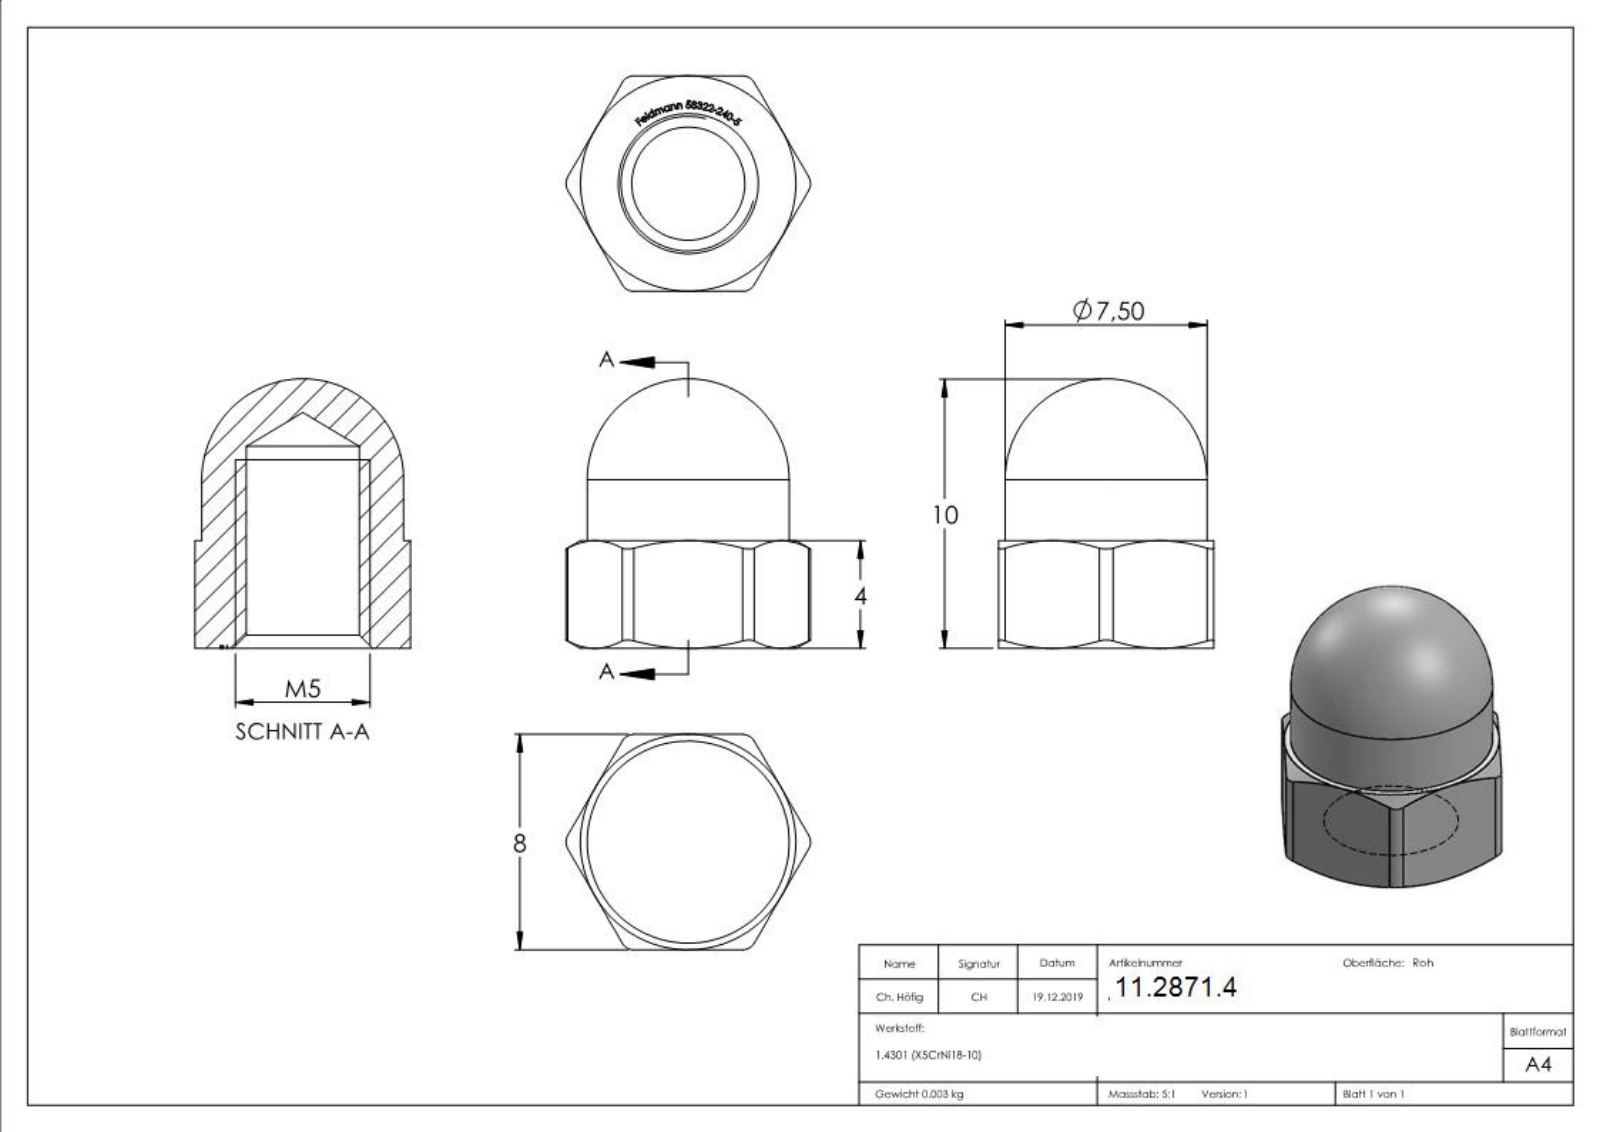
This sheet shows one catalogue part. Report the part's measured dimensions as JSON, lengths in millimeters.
{"part_name": "58322-240-5", "step_written_by": "SolidWorks 2015 (CONFIG_CONTROL_DESIGN)", "units": "millimeters", "bodies": {"solids": 1, "faces": 287, "planar": 142, "cylindrical": 8, "other": 137}, "overall_size": [15, 9.08, 8], "volume_mm3": 319, "surface_area_mm2": 412, "round_holes": [[4.2, 1]], "round_bosses_or_shafts": [[7.5, 1]], "partial_cylinders_radius": [[0.5, 6]], "face_to_face_distances": [8, 4, 3.9]}
